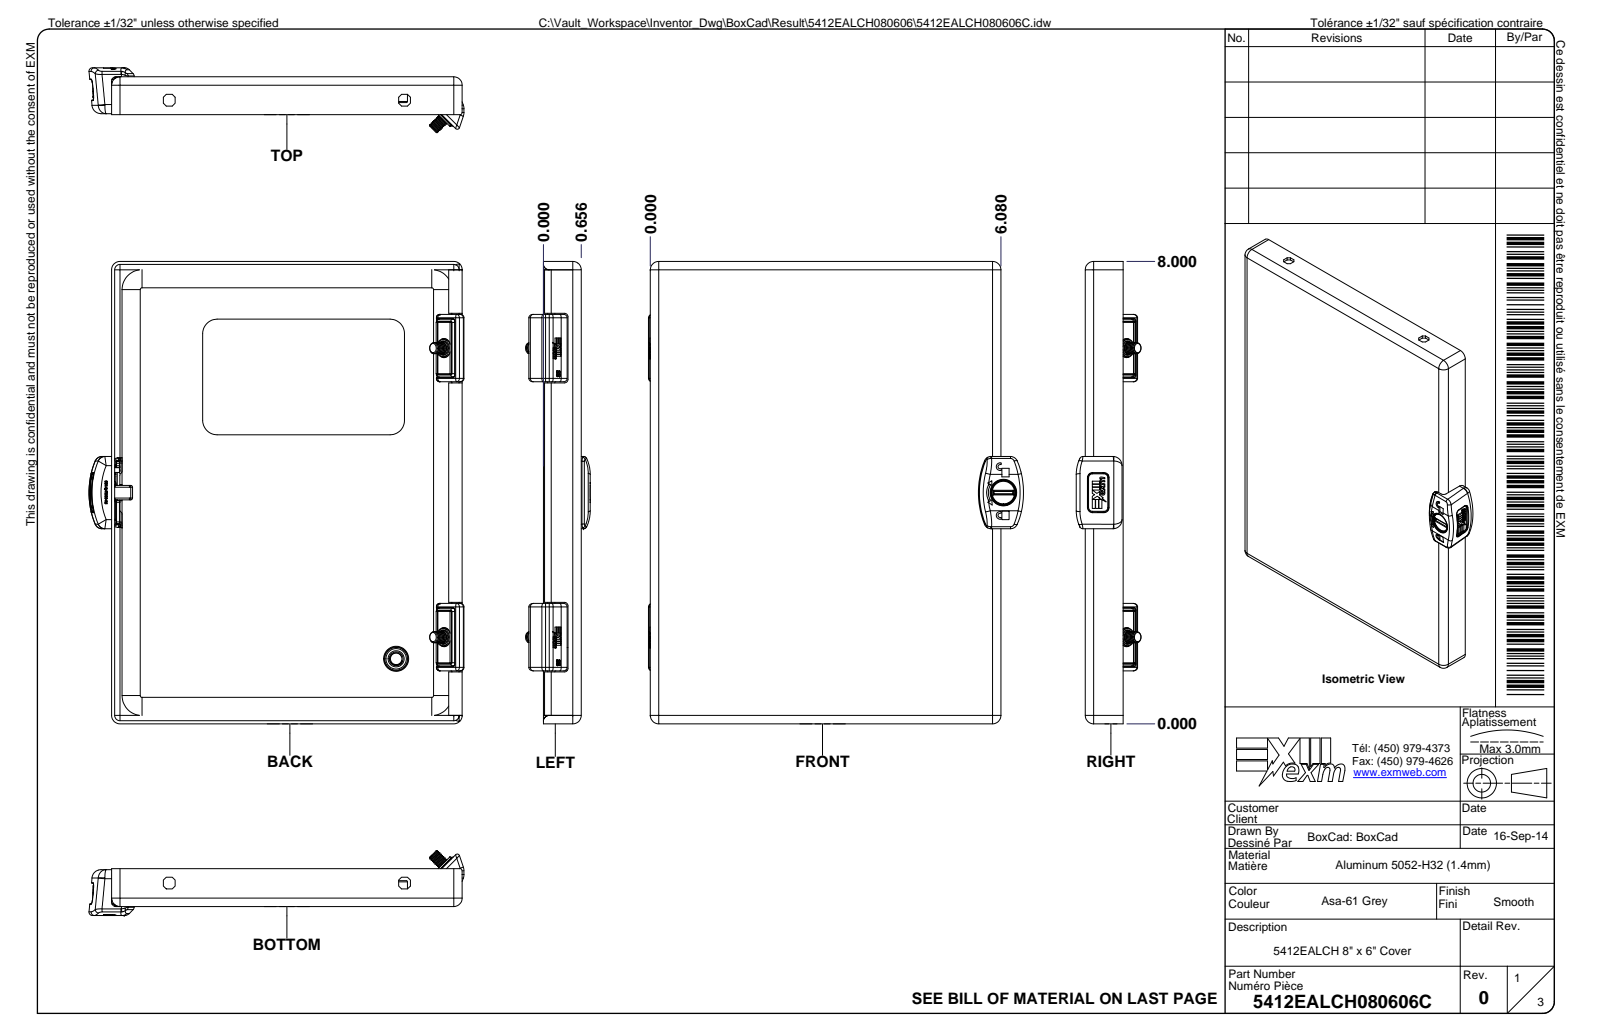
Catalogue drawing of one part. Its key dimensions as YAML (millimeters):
part_name: "5412EALCH080606; 5412EALCH080606B; 5412EALCH080606B-P; RIVET_NUT_SS_M6_FH_CE (+8 more)"
step_written_by: "Autodesk Inventor 2024 (AUTOMOTIVE_DESIGN)"
units: millimeters
bodies: {solids: 50, faces: 6272, planar: 2802, cylindrical: 1470, other: 2000}
overall_size: [241.2, 171.6, 163.6]
volume: 342500
surface_area: 485900
round_holes:
  - {diameter: 5, count: 6}
  - {diameter: 5, count: 4}
  - {diameter: 6, count: 4}
  - {diameter: 8.1, count: 4}
  - {diameter: 0.8, count: 2}
  - {diameter: 4.2, count: 2}
  - {diameter: 4.4, count: 2}
  - {diameter: 4.4, count: 2}
  - {diameter: 5.1, count: 2}
  - {diameter: 5.5, count: 2}
  - {diameter: 5.8, count: 2}
  - {diameter: 6, count: 2}
round_bosses_or_shafts:
  - {diameter: 5.9, count: 8}
  - {diameter: 12.7, count: 4}
  - {diameter: 6, count: 4}
  - {diameter: 5, count: 3}
  - {diameter: 10, count: 2}
  - {diameter: 7.6, count: 2}
  - {diameter: 4.9, count: 2}
  - {diameter: 0.9, count: 2}
partial_cylinders:
  - {radius: 0.5, count: 175}
  - {radius: 0.2, count: 157}
  - {radius: 0.3, count: 88}
  - {radius: 1, count: 77}
  - {radius: 0.1, count: 70}
  - {radius: 1.5, count: 56}
  - {radius: 0.8, count: 31}
  - {radius: 0.3, count: 24}
face_to_face_distances: [1.3, 163.3, 151.1, 201.9, 162, 164.6, 152.4, 149.7, 203.2, 200.5]
hole_center_spacings: [105.6, 13.8, 108, 158.8, 172.3, 192, 201.6, 154.3]
